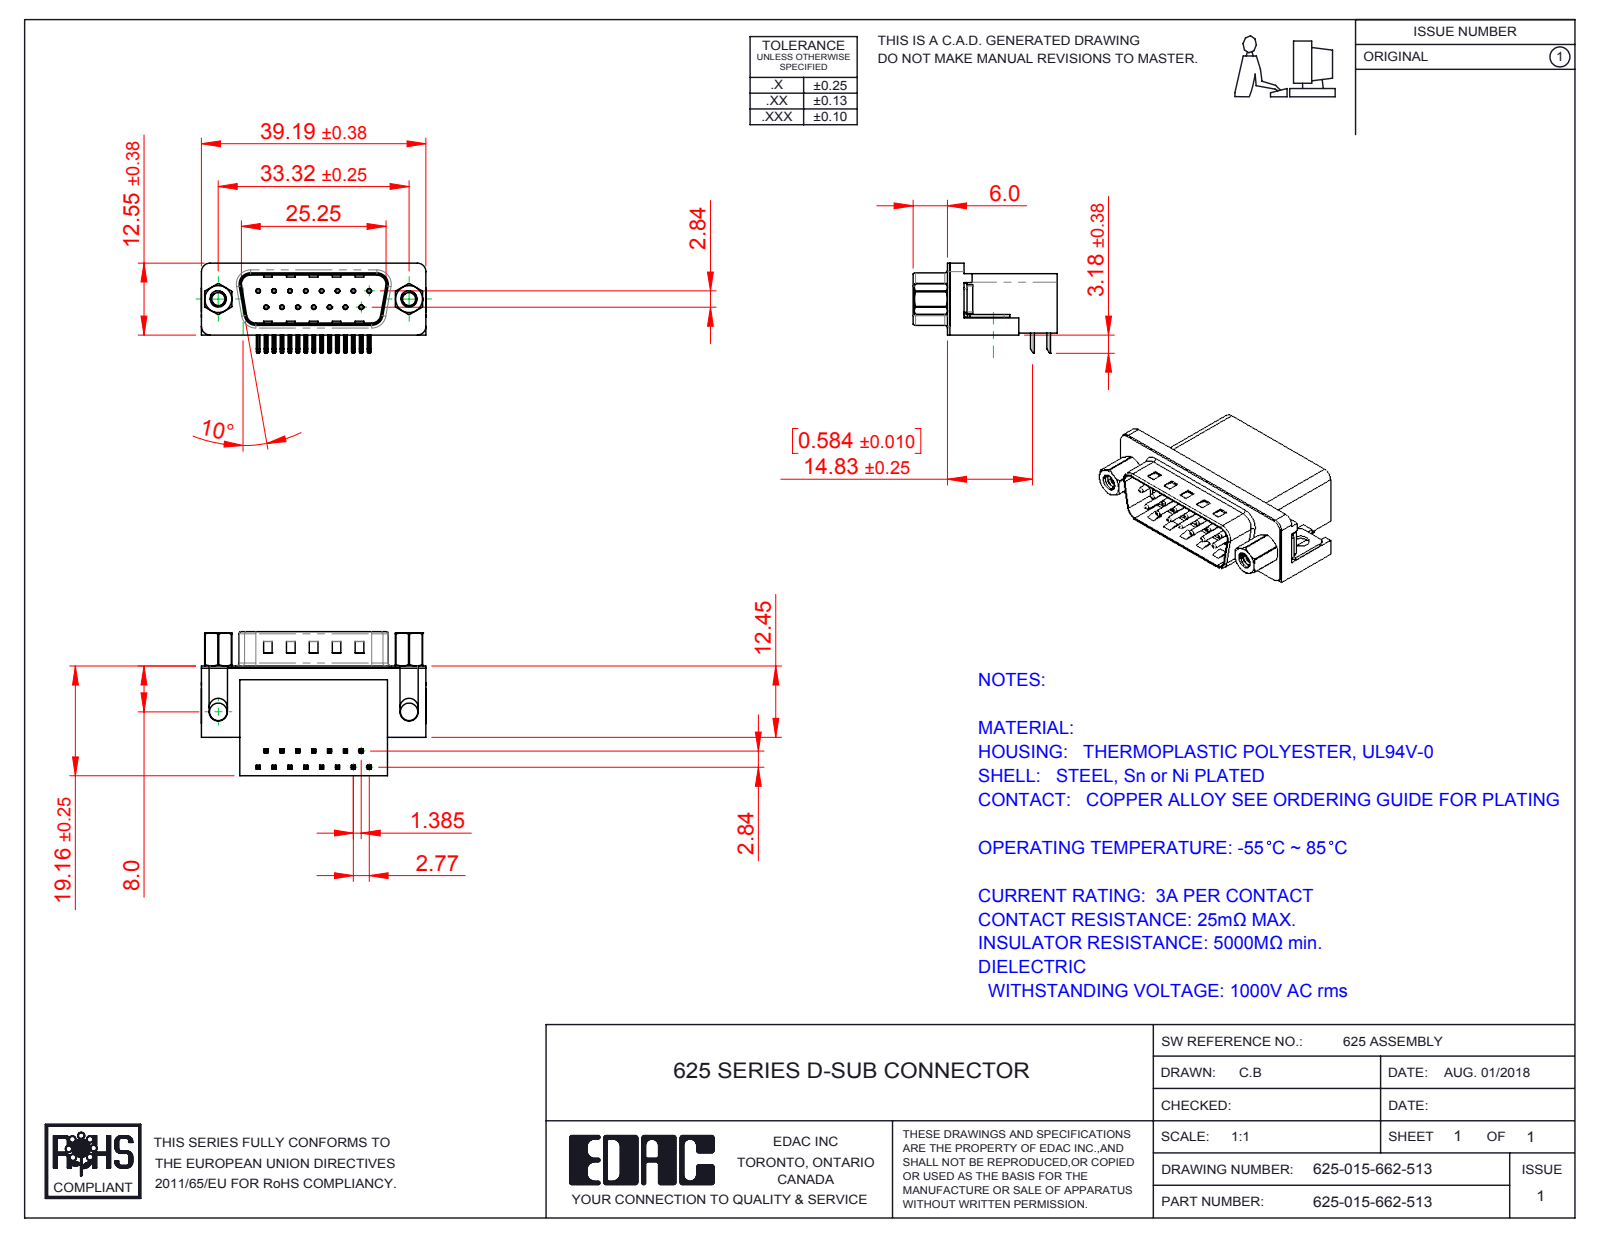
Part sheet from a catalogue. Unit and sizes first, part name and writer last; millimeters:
Units: millimetres
Overall size (bounding box): 39.22 × 25.16 × 15.73
Round holes (diameter × count): ⌀0.35 ×15, ⌀0.8 ×15, ⌀2.26 ×2, ⌀2.29 ×2, ⌀3.05 ×2, ⌀4 ×2, ⌀4.8 ×2, ⌀5 ×2
Round bosses / shafts (diameter × count): ⌀0.75 ×15, ⌀4.9 ×2, ⌀4.75 ×2, ⌀3.9 ×2, ⌀2.79 ×2
Partial cylindrical surfaces — rounded edges, fillets, slot ends (radius × count): R0.25 ×68, R0.12 ×30, R1 ×16, R0.5 ×9, R1.6 ×8, R1.5 ×6, R0.9 ×4, R2 ×4
Main face-to-face distances: 0.4, 10.35, 18.76, 2.1, 19.16, 10.46, 1.7, 10.86, 8.76, 16.26
Hole centre spacings: 3.16, 2.77, 5.54, 8.31, 11.08, 5.03, 5.04, 7.48
Volume: 6 454 mm³ · Surface area: 6 895 mm²
Bodies: 23 solids, 1605 faces (915 planar, 519 cylindrical, 171 other)
Part name (STEP PRODUCT): 625 Housing_15 Socket; 625 Shell_15 Socket; 625 4-40 Hex Standoff 5; 625 Contact Bottom (+4 more)
STEP written by: SolidWorks 2016 (CONFIG_CONTROL_DESIGN)
